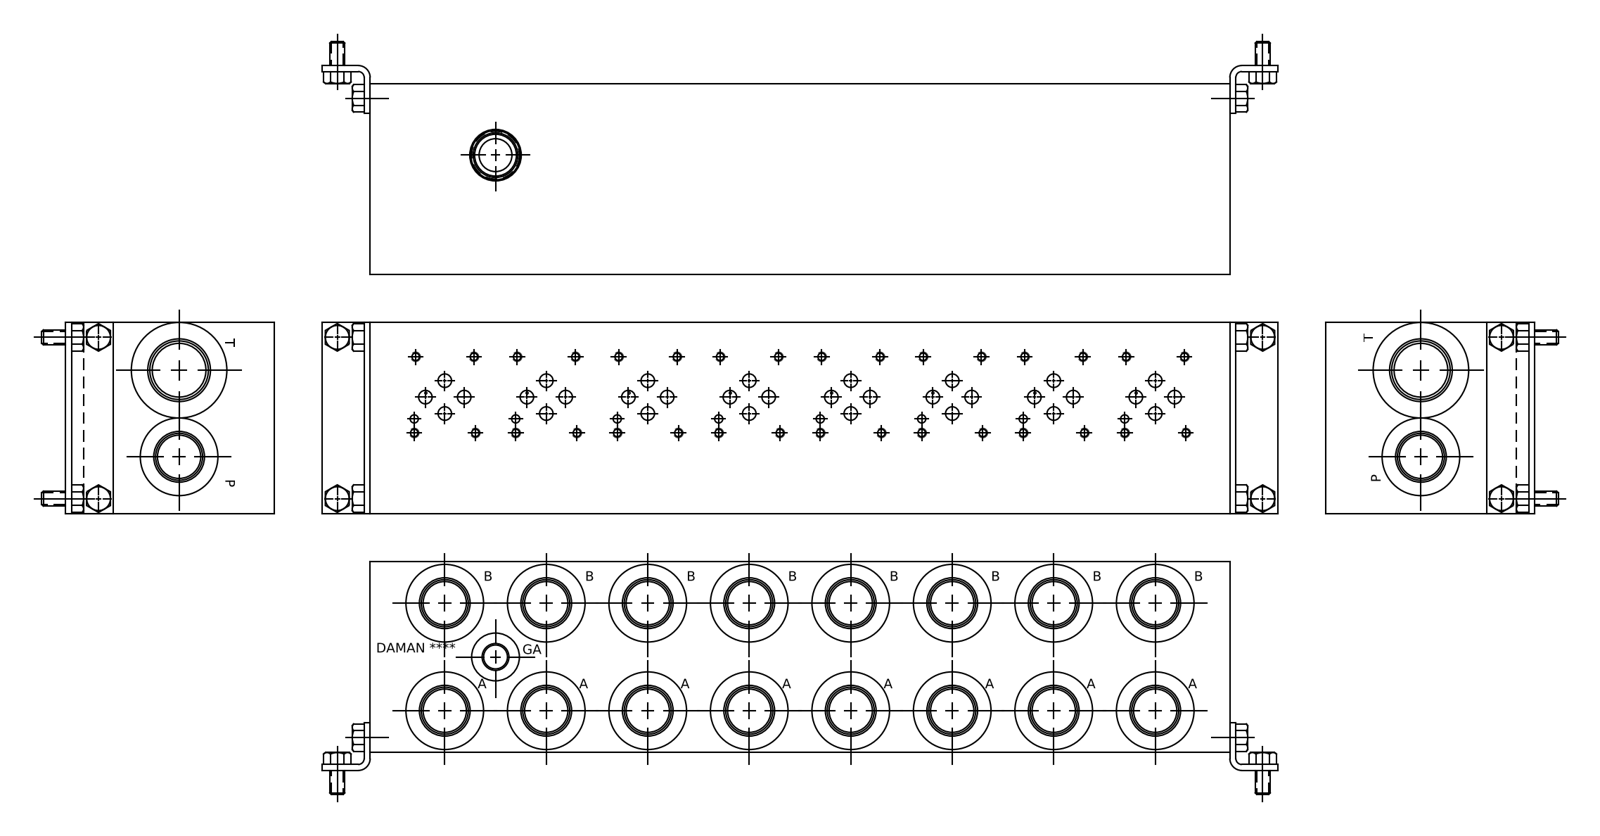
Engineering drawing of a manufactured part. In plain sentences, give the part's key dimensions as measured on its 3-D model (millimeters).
The part is named "Part_AD03HP082S_S_3D". Its 3-D file was written by "Autodesk Inventor 2021 (AUTOMOTIVE_DESIGN)". It is 1 solid with 1255 faces: 579 planar, 232 cylindrical and 444 other. Overall it measures 457.2 by 101.6 by 101.6 millimeters. Its volume is 4 297 000 cubic millimeters and its surface area 276 394 square millimeters. Round holes: 32 of diameter 3.78, 32 of diameter 4.83, 24 of diameter 6.35, 17 of diameter 23.01, 17 of diameter 24.92, 17 of diameter 27.43, 17 of diameter 42.04, 16 of diameter 27, 8 of diameter 3.96, 8 of diameter 7.14, 8 of diameter 10.72, 2 of diameter 6.53. The main face-to-face distances are 101.6, 0.79, 100.81, 457.2, 456.41, 19.84, 19.05, 455.62, 81.76, 0.75. The hole center spacings are 107.95, 53.98, 215.9, 53.97, 161.93, 13.54, 13.52, 78.61.
